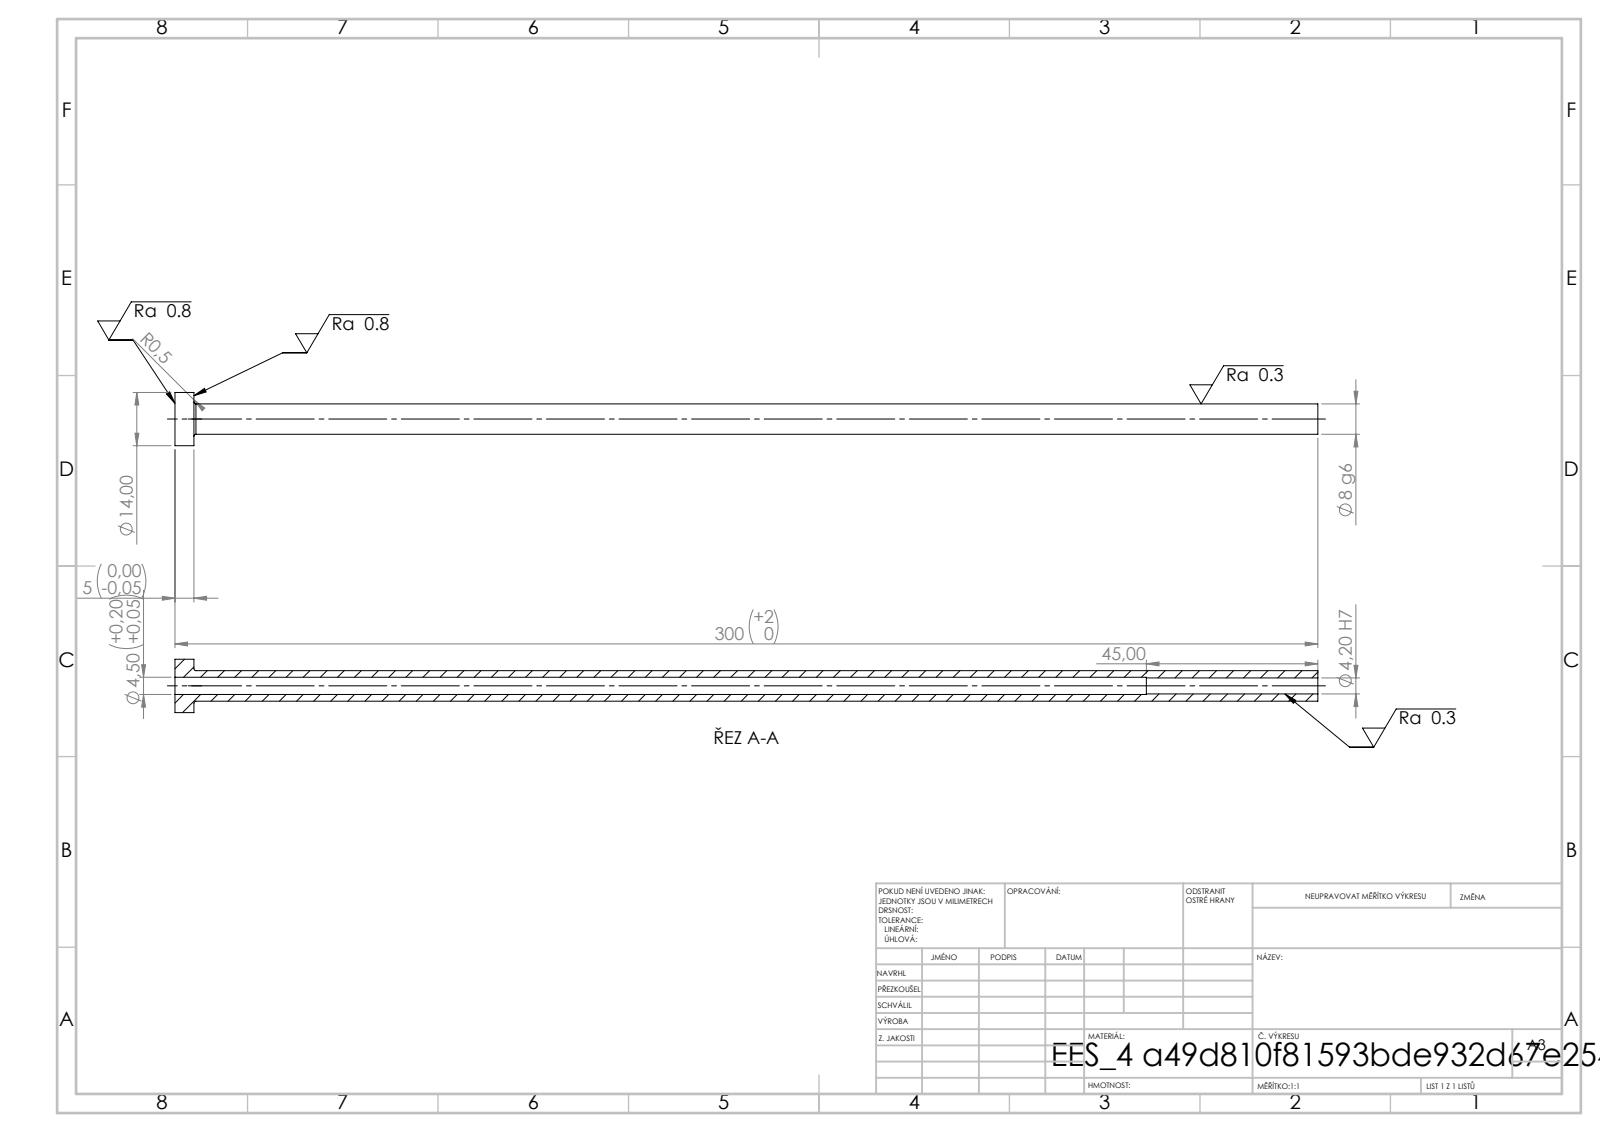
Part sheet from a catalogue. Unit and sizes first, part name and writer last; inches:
Units: inches
Overall size (bounding box): 11.811 × 0.551 × 0.551
Round holes (diameter × count): ⌀0.165 ×1, ⌀0.177 ×1
Round bosses / shafts (diameter × count): ⌀0.551 ×1, ⌀0.315 ×1
Main face-to-face distances: 0.197, 11.811, 11.614, 10.039, 9.843, 1.772
Volume: 0.666 in³ · Surface area: 18.77 in²
Bodies: 1 solid, 14 faces (4 planar, 8 cylindrical, 2 other)
STEP written by: SolidWorks 2019 (CONFIG_CONTROL_DESIGN)
